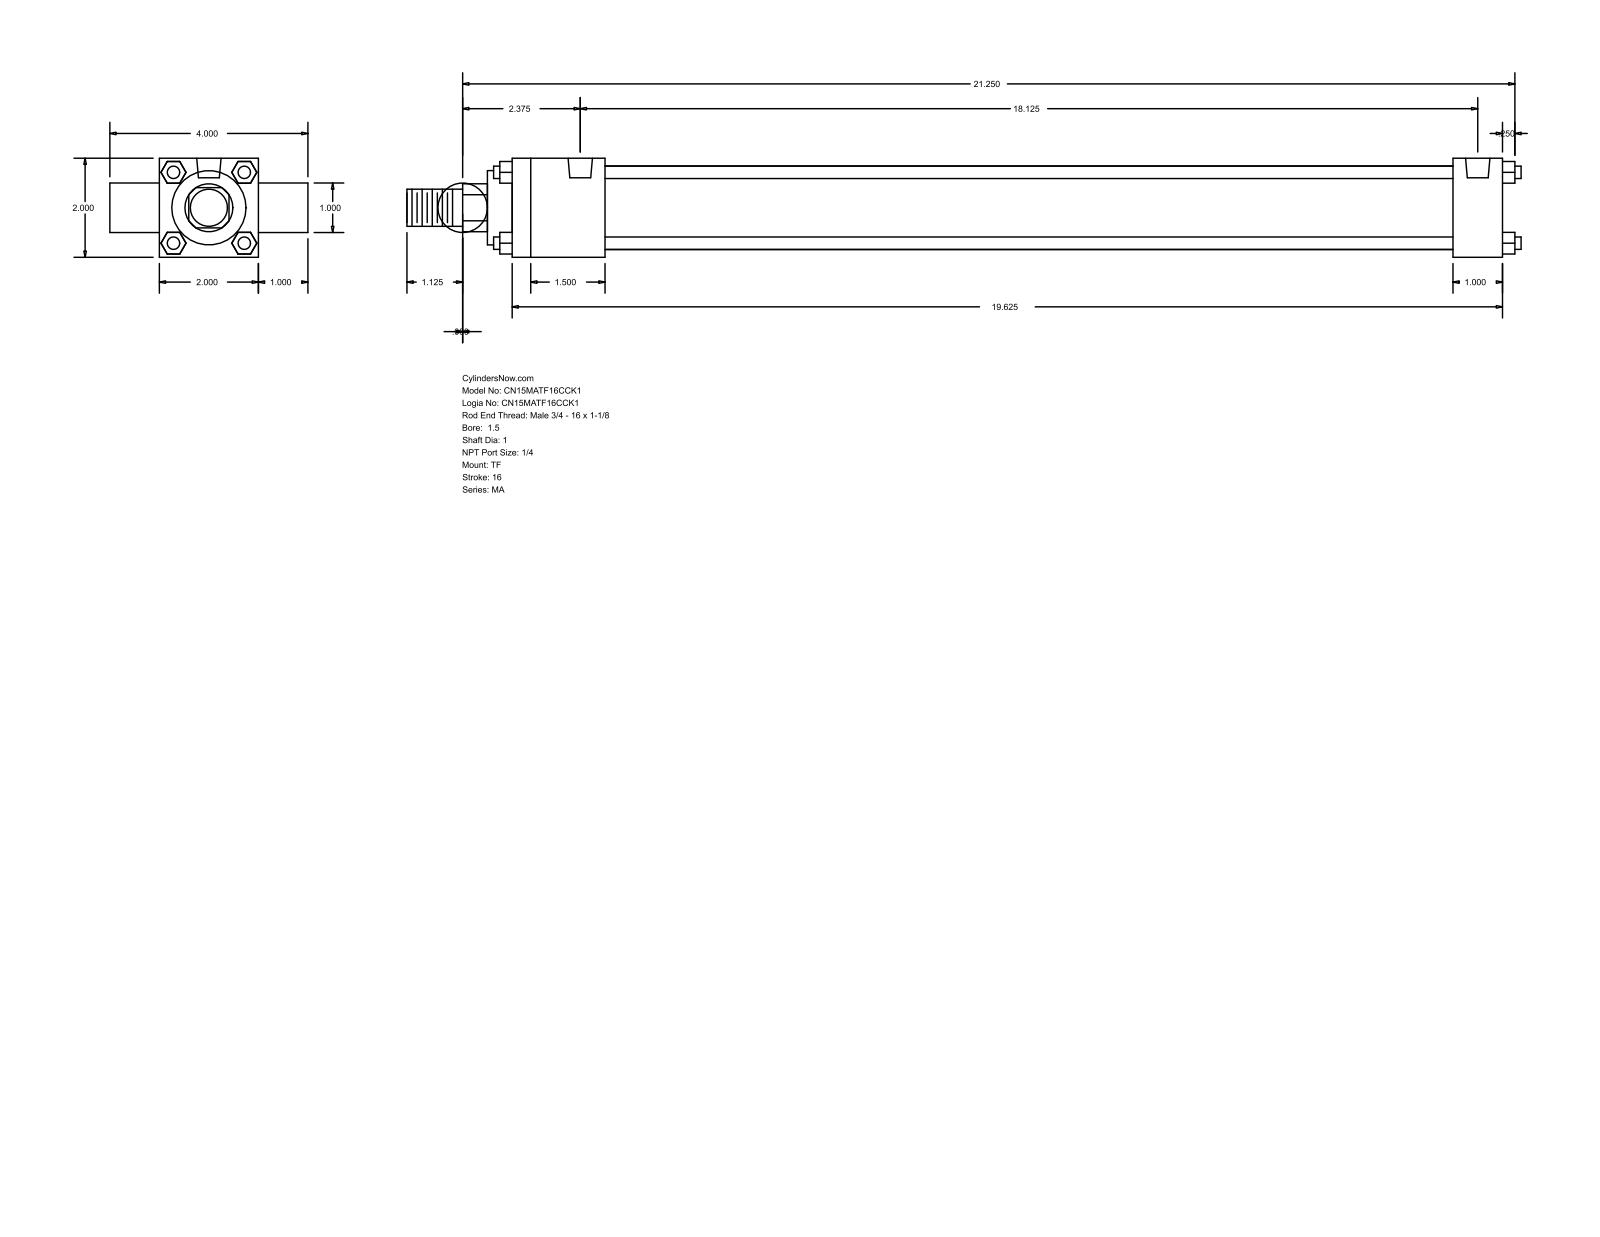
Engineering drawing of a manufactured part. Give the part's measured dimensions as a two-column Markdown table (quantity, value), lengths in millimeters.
| quantity | value |
| --- | --- |
| part name | MA_TF__0150_1 |
| STEP written by | GSSL Pune (CONFIG_CONTROL_DESIGN) |
| units | millimeters |
| bodies | 0 solids, 120 faces (92 planar, 28 cylindrical, 0 other) |
| overall size | 571.5 × 101.6 × 50.8 |
| round holes (diameter × count) | 7.94 × 3, 12.49 × 2 |
| round bosses / shafts (diameter × count) | 6.35 × 4, 25.4 × 2, 42.93 × 1, 38.1 × 1, 19.05 × 1 |
| partial cylindrical surfaces (radius × count) | 12.29 × 1 |
| main face-to-face distances | 50.8, 25.4, 508, 76.2, 6.35, 47.63, 482.6, 434.97, 460.37, 520.7 |
| hole center spacings | 460.37 |
